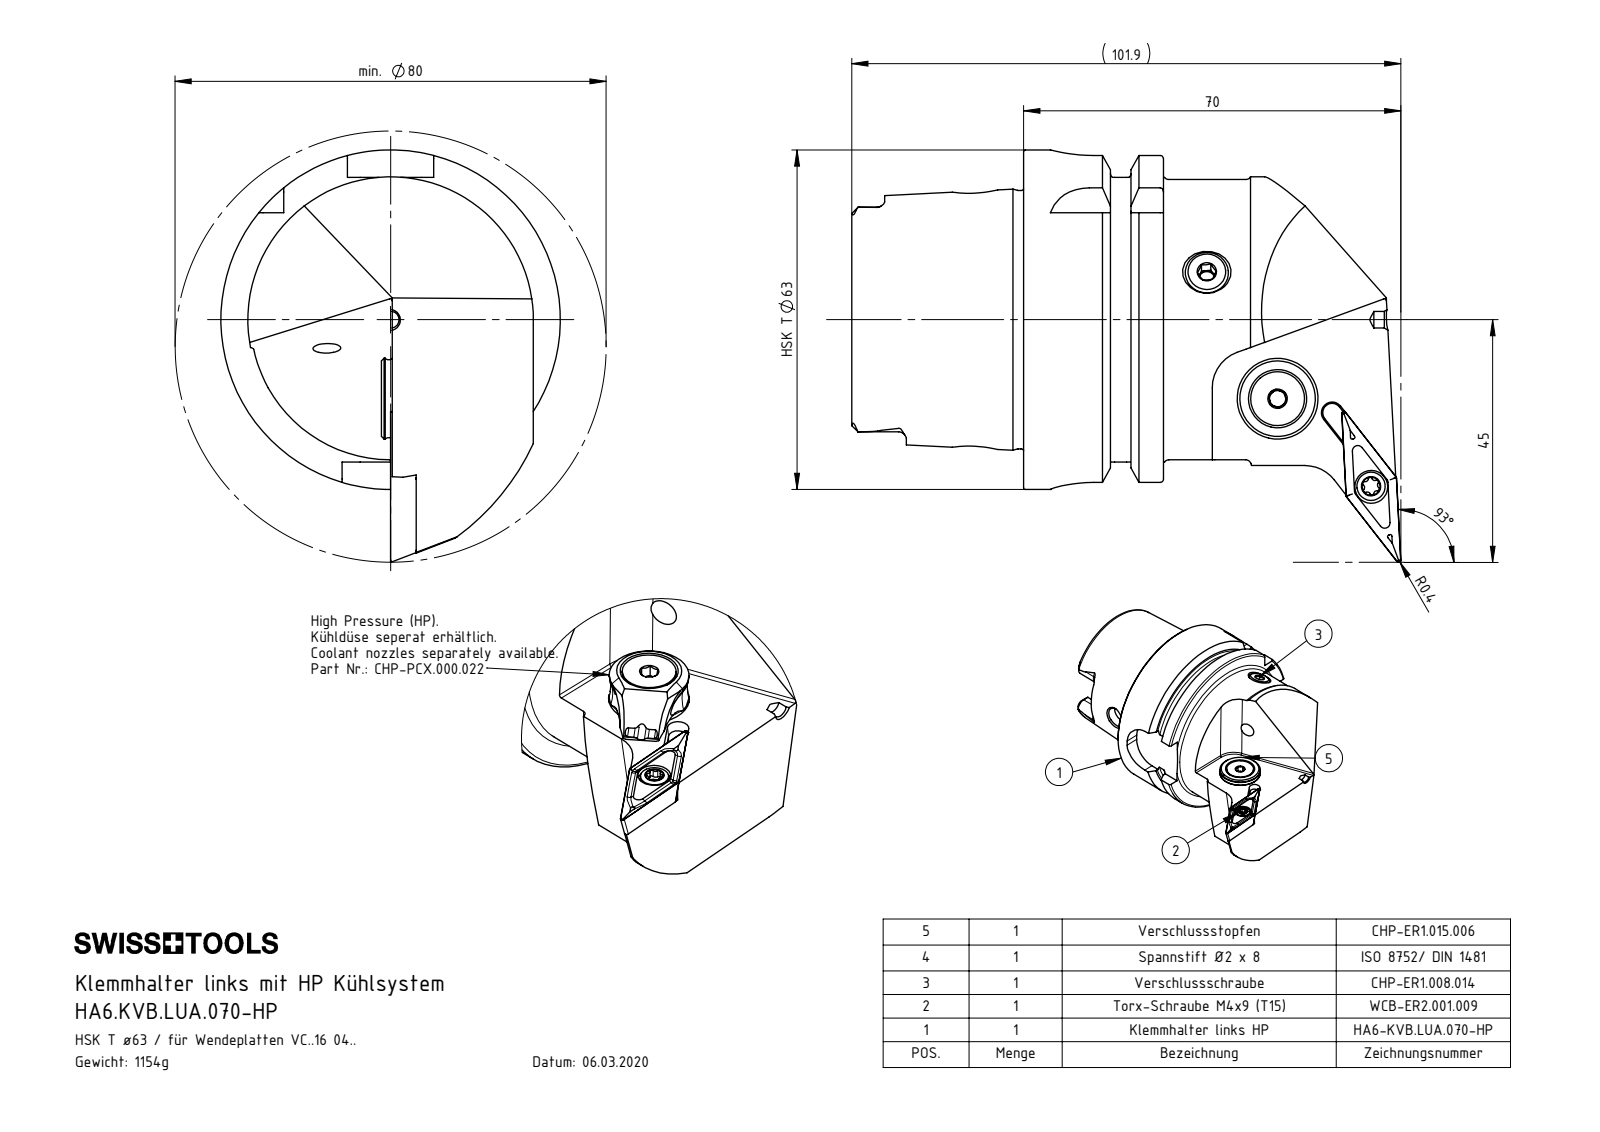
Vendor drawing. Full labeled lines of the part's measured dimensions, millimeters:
Part name (STEP PRODUCT): ISO 8752 2x8; DIN 7991 - M5x15; DIN 3771 - 13x1; HA6-KVB.LUA.070-HP_A (+6 more)
STEP written by: SolidWorks 2017 (AUTOMOTIVE_DESIGN)
Units: millimetres
Bodies: 8 solids, 425 faces (121 planar, 120 cylindrical, 184 other)
Overall size (bounding box): 101.9 × 76.5 × 63
Volume: 146 459 mm³ · Surface area: 33 274 mm²
Round holes (diameter × count): ⌀4.2 ×2, ⌀5 ×2, ⌀1.2 ×1, ⌀2 ×1, ⌀2.5 ×1, ⌀3 ×1, ⌀3.3 ×1, ⌀4.4 ×1, ⌀5.2 ×1, ⌀6.1 ×1, ⌀7 ×1, ⌀7.5 ×1
Round bosses / shafts (diameter × count): ⌀63 ×1, ⌀54.95 ×1, ⌀52 ×1, ⌀47.94 ×1, ⌀15 ×1, ⌀13.4 ×1, ⌀10 ×1, ⌀8 ×1
Partial cylindrical surfaces — rounded edges, fillets, slot ends (radius × count): R0.34 ×6, R0.59 ×6, R1.4 ×6, R8 ×4, R0.5 ×2, R2.82 ×2, R2.88 ×2, R7 ×2
Main face-to-face distances: 25.95, 16, 9.95, 26.2, 31.9, 41.85, 57.85, 52.8, 21.8, 11.85
Hole centre spacings: 4.5, 20.01, 20.12, 23.77, 23.88, 42.72, 47.19, 65.26
